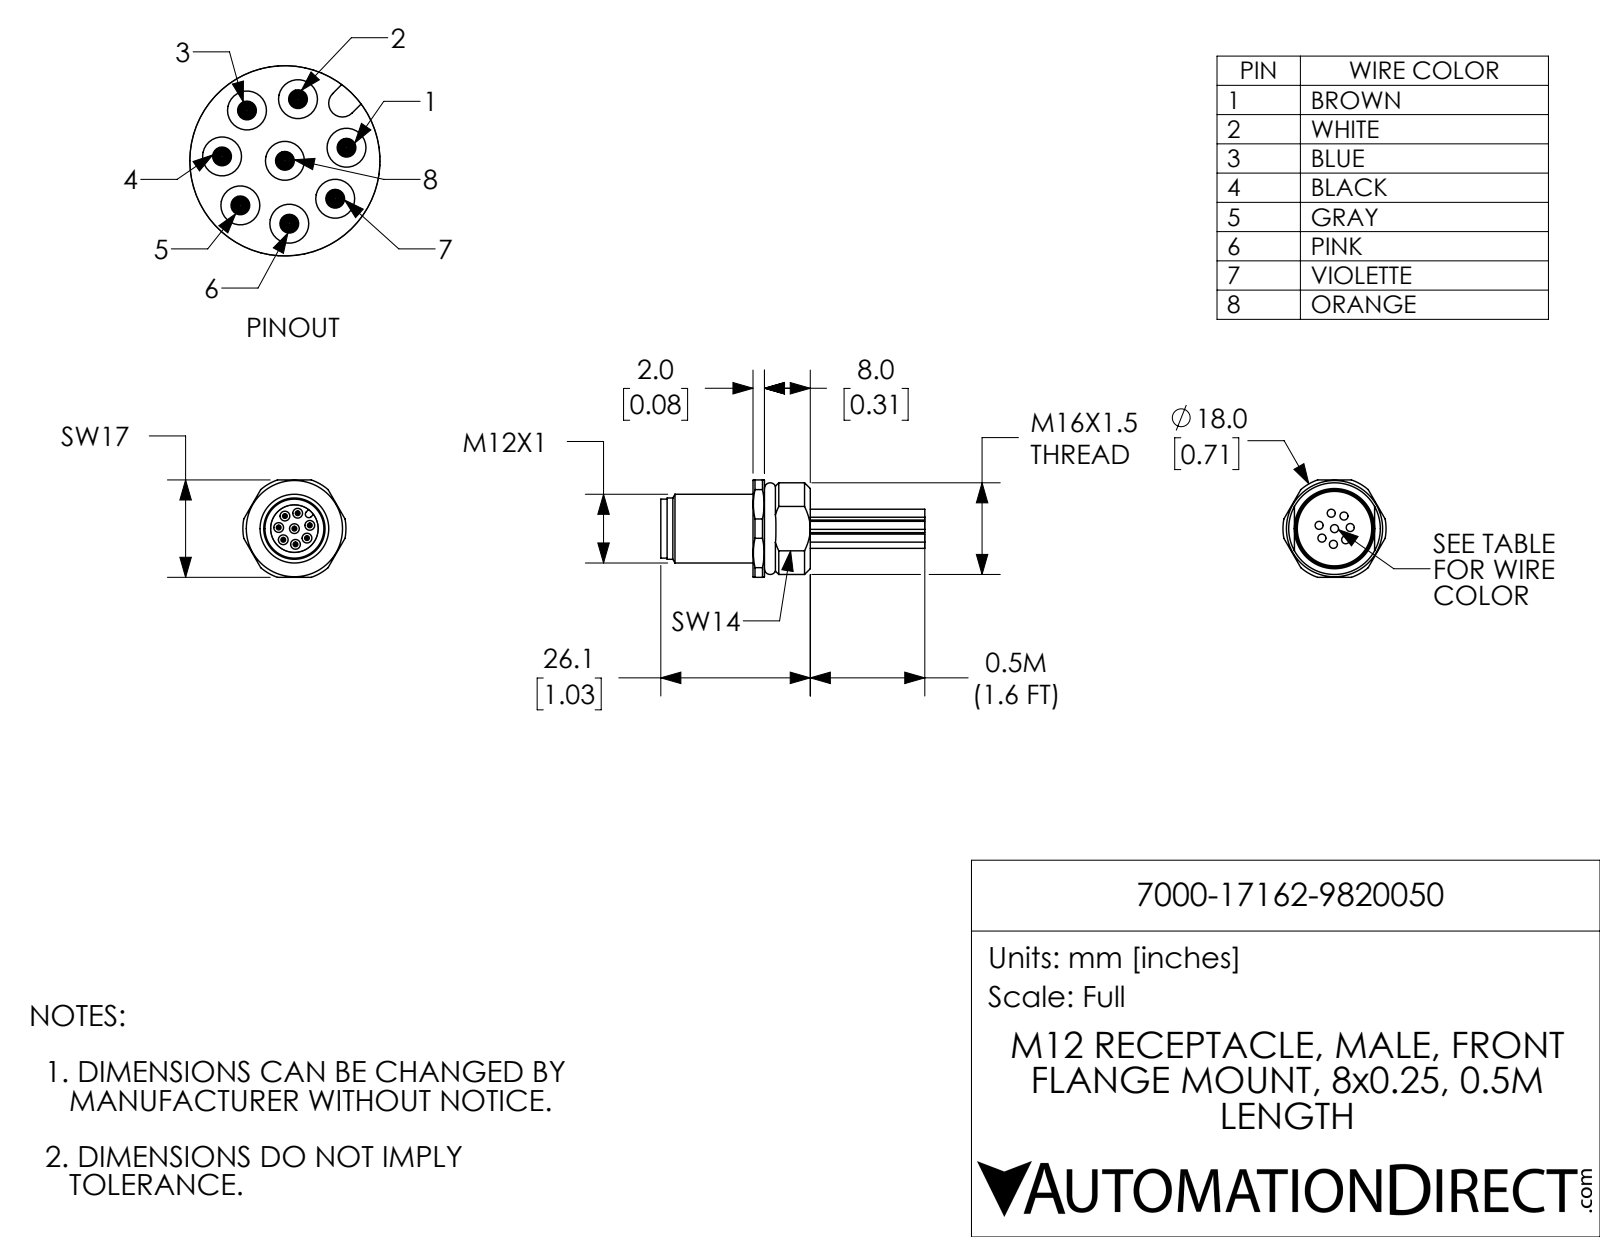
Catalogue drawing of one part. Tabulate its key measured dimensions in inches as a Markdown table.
| quantity | value |
| --- | --- |
| part name | 7000-17162-9820050 |
| STEP written by | SolidWorks 2017 (AUTOMOTIVE_DESIGN) |
| units | inches |
| bodies | 1 solid, 142 faces (42 planar, 68 cylindrical, 32 other) |
| overall size | 1.815 × 0.709 × 0.669 |
| volume | 0.209 in³ |
| surface area | 4.364 in² |
| round holes (diameter × count) | 0.067 × 8, 0.327 × 1, 0.512 × 1 |
| round bosses / shafts (diameter × count) | 0.055 × 8, 0.032 × 8, 0.472 × 1, 0.421 × 1, 0.406 × 1 |
| partial cylindrical surfaces (radius × count) | 0.024 × 1, 0.315 × 1, 0.354 × 1 |
| main face-to-face distances | 0.354, 0.276, 0.079, 0.551, 0.669, 0.638, 0.362, 0.283, 0.35, 0.988 |
| hole center spacings | 0.108, 0.163, 0.207, 0.214, 0.089, 0.09, 0.09, 0.183 |
